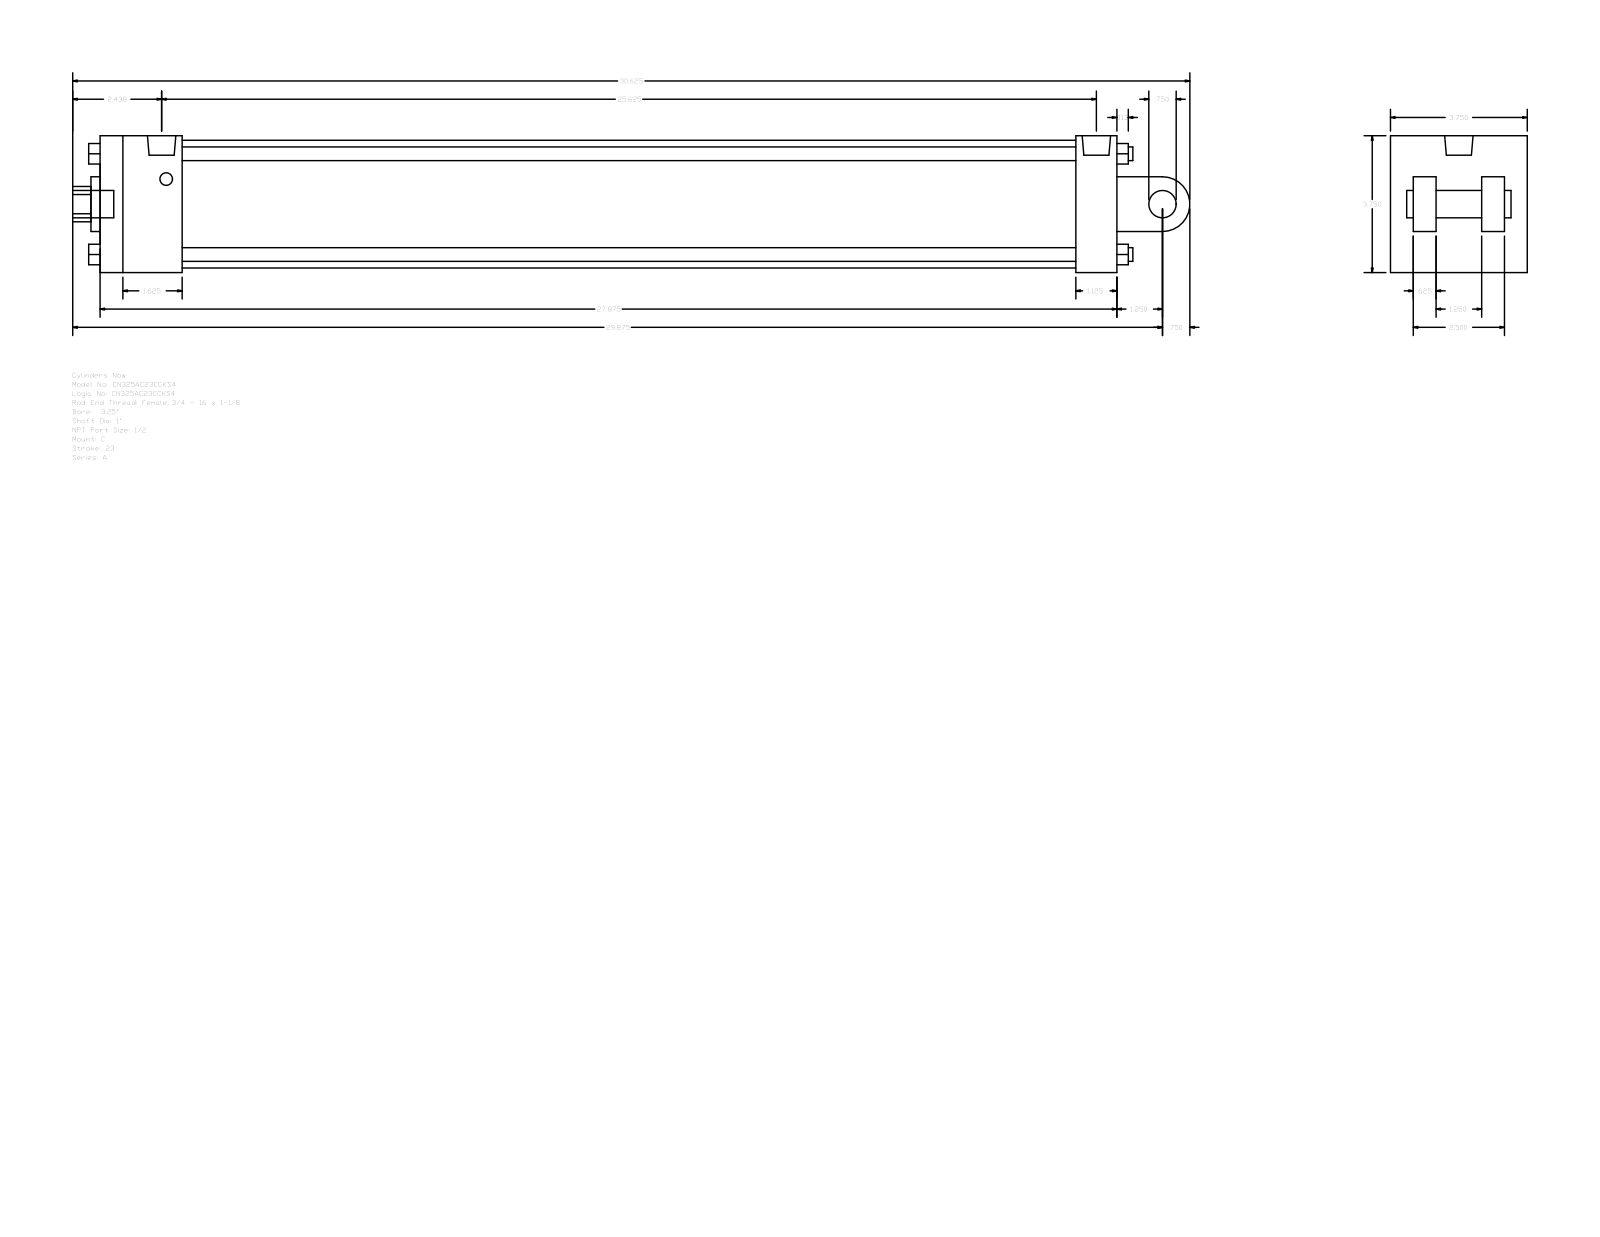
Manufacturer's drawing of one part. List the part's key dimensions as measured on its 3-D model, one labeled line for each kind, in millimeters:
Part name (STEP PRODUCT): A_C__0325_1
STEP written by: GSSL Pune (CONFIG_CONTROL_DESIGN)
Units: millimetres
Bodies: 0 solids, 135 faces (102 planar, 33 cylindrical, 0 other)
Overall size (bounding box): 777.88 × 95.25 × 95.25
Round holes (diameter × count): ⌀8.73 ×2, ⌀19.77 ×1, ⌀25.4 ×1, ⌀38.1 ×1, ⌀88.9 ×1
Round bosses / shafts (diameter × count): ⌀9.53 ×4, ⌀19.05 ×2, ⌀8.73 ×2, ⌀19.77 ×1
Partial cylindrical surfaces — rounded edges, fillets, slot ends (radius × count): R12.29 ×1, R19.05 ×1
Main face-to-face distances: 95.24, 708.03, 15.87, 63.5, 47.63, 31.74, 79.37, 66.67, 679.45, 28.58
Hole centre spacings: 3.18
